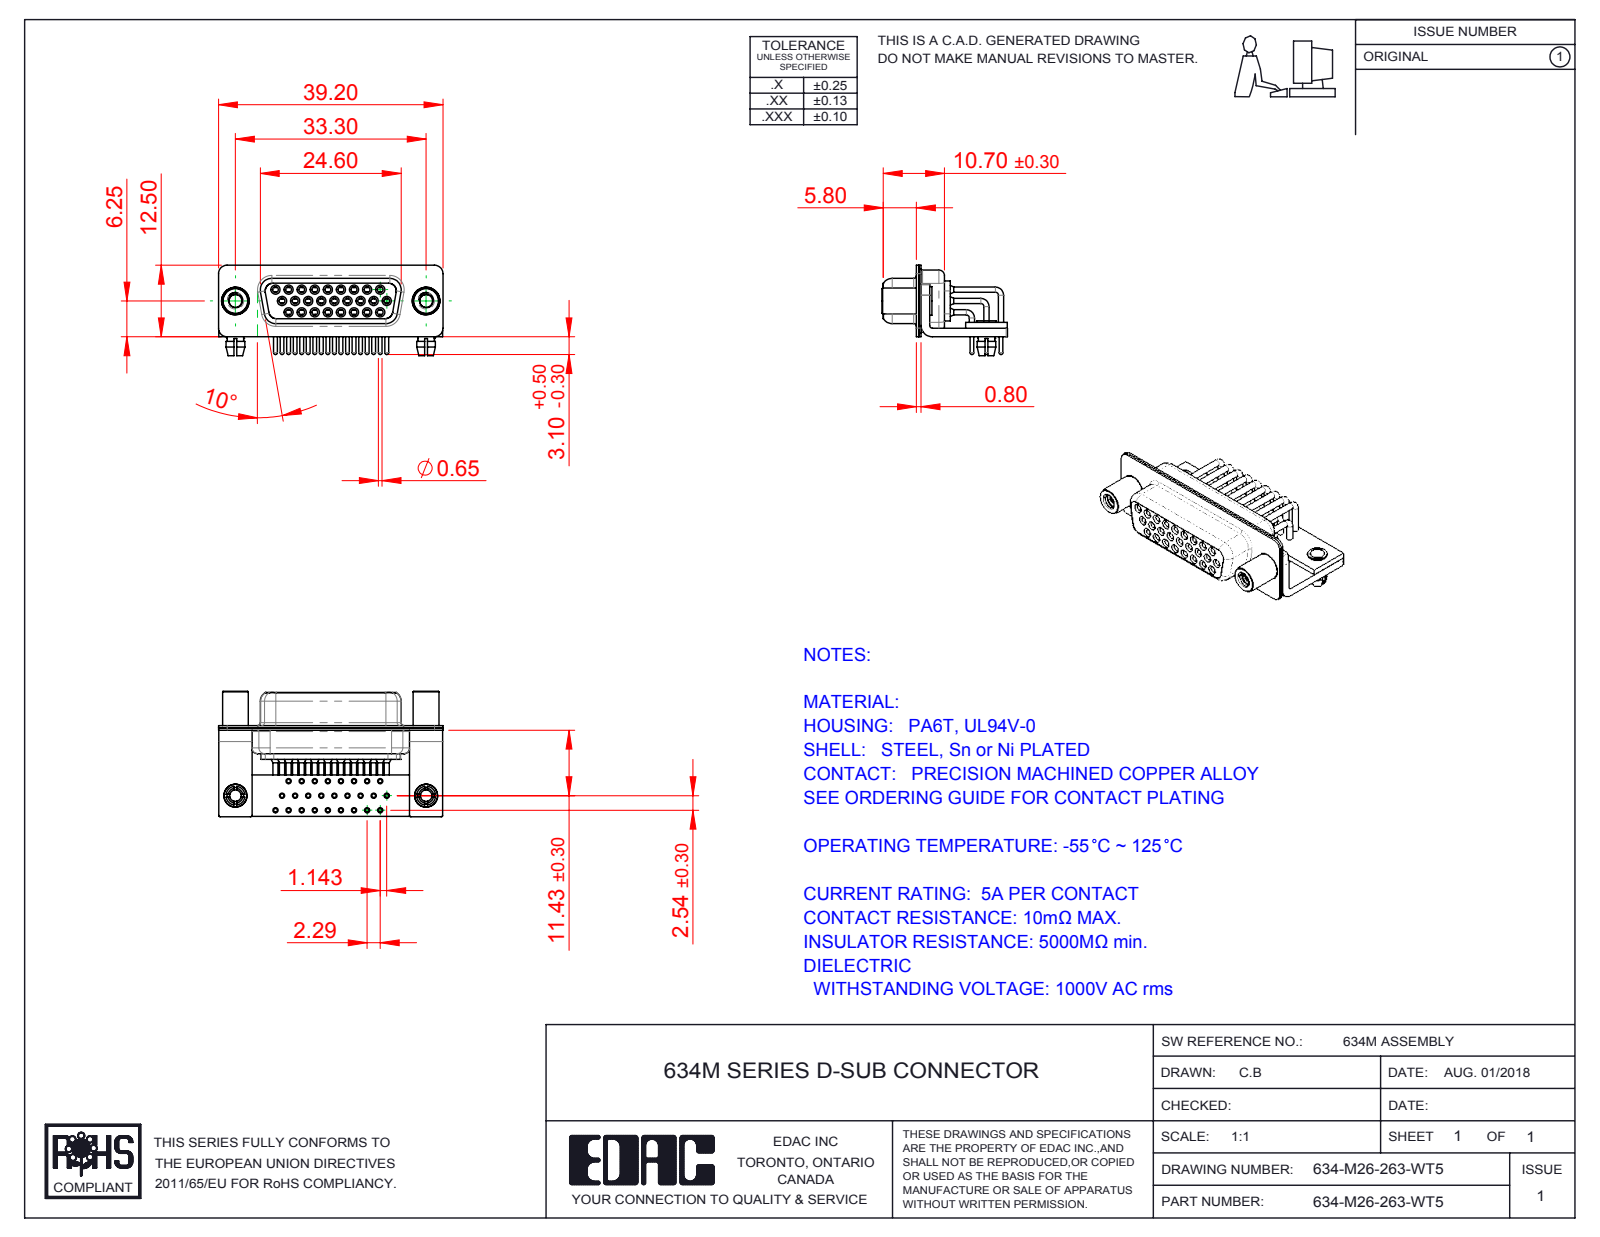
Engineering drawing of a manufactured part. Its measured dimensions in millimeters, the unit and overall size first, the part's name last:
Units: millimetres
Overall size (bounding box): 39.2 × 21.9 × 15.8
Round holes (diameter × count): ⌀2 ×28, ⌀0.9 ×26, ⌀1 ×26, ⌀1.1 ×26, ⌀1.7 ×26, ⌀1.8 ×26, ⌀2.26 ×2, ⌀2.5 ×2, ⌀3.2 ×2, ⌀4 ×2, ⌀4.8 ×2
Round bosses / shafts (diameter × count): ⌀0.9 ×27, ⌀1.6 ×26, ⌀1.5 ×26, ⌀0.65 ×26, ⌀5 ×2, ⌀4.9 ×2, ⌀4.5 ×2, ⌀4 ×2
Partial cylindrical surfaces — rounded edges, fillets, slot ends (radius × count): R0.25 ×16, R1.5 ×16, R2 ×13, R1.35 ×8, R1.6 ×8, R0.5 ×5, R0.6 ×4, R0.65 ×4
Main face-to-face distances: 0.4, 2.3, 1.9, 0.8, 1.5, 1, 9.35, 8.5, 1.45, 8.95
Hole centre spacings: 4.57, 2.29, 2.28, 3.96, 6.05, 6.86, 4.27, 2.78
Volume: 3 236 mm³ · Surface area: 10 333 mm²
Bodies: 36 solids, 1901 faces (533 planar, 883 cylindrical, 485 other)
Part name (STEP PRODUCT): 634M 4-40 Threaded Standoff; 634M Stabilizer Bracket; 634M Contact Row 3; 634M Contact Row 2 (+7 more)
STEP written by: SolidWorks 2016 (CONFIG_CONTROL_DESIGN)
